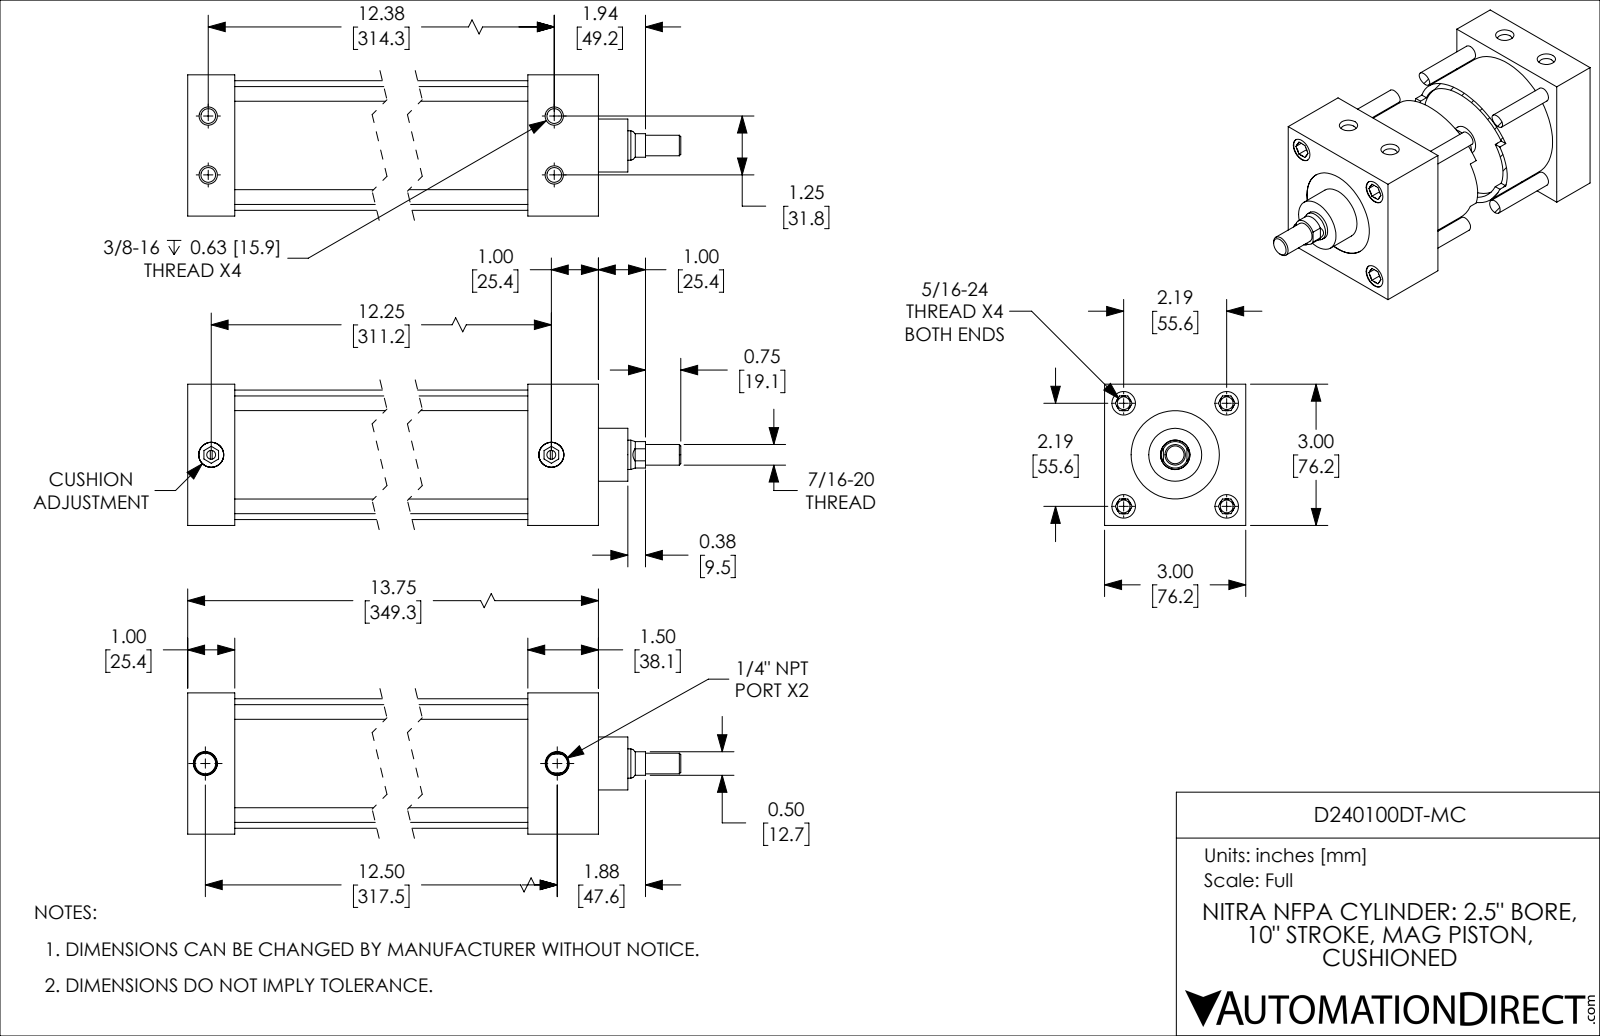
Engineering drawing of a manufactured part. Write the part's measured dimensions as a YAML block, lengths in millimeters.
part_name: "D240100DT-MC; D240100DT-MC_BODY; D240100DT-MC_PISTON_KK1; D240100DT-MC_CUSHION"
step_written_by: "SolidWorks 2019 (CONFIG_CONTROL_DESIGN)"
units: millimeters
bodies: {solids: 4, faces: 248, planar: 90, cylindrical: 78, other: 80}
overall_size: [393.7, 76.2, 76.2]
volume: 760900
surface_area: 231000
round_holes:
  - {diameter: 6.9, count: 4}
  - {diameter: 8, count: 4}
  - {diameter: 12.7, count: 4}
  - {diameter: 4.8, count: 2}
  - {diameter: 11.1, count: 2}
  - {diameter: 13.5, count: 2}
  - {diameter: 15.9, count: 1}
  - {diameter: 47.6, count: 1}
  - {diameter: 63.5, count: 1}
round_bosses_or_shafts:
  - {diameter: 7.9, count: 4}
  - {diameter: 13.5, count: 2}
  - {diameter: 69.9, count: 1}
  - {diameter: 63.5, count: 1}
  - {diameter: 28.6, count: 1}
  - {diameter: 15.8, count: 1}
  - {diameter: 11.1, count: 1}
partial_cylinders:
  - {radius: 7.1, count: 1}
face_to_face_distances: [76.2, 25.4, 311.2, 285.8, 349.3, 323.9, 38.1, 31.8, 57.2, 254]
hole_center_spacings: [39.3, 55.6, 316.3, 16, 16, 31.8, 78.7, 314.3]
